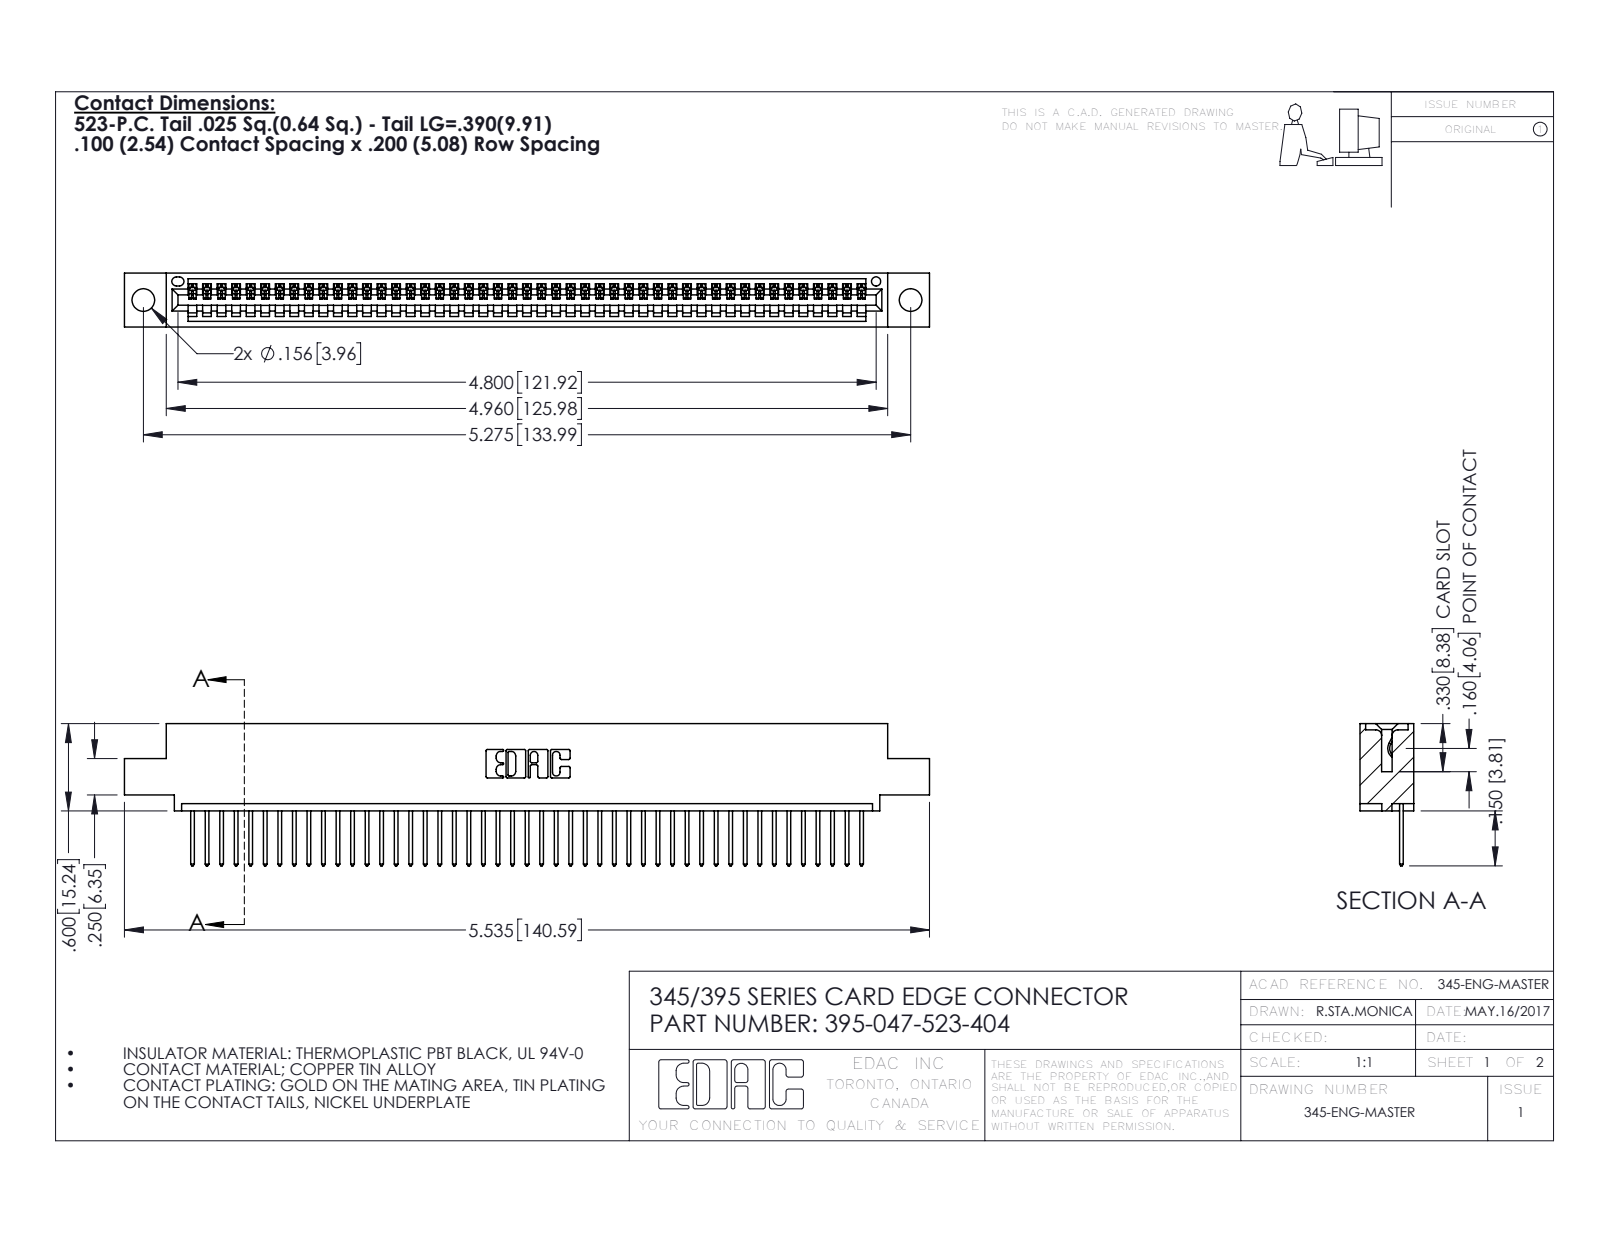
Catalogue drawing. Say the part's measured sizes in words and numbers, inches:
The part is named "345 Part_0.110 Offset - 0.156 Dia-TH; 345-292-001_345-293-123; 395-047-523-404". Its 3-D file was written by "SolidWorks 2016 (CONFIG_CONTROL_DESIGN)". It is 48 solids with 2856 faces: 1964 planar, 892 cylindrical and 0 other. Overall it measures 5.535 by 0.977 by 0.37 inches. Its volume is 0.806 cubic inches and its surface area 27.24 square inches. Round holes: 2 of diameter 0.156, 1 of diameter 0.064. Partial cylindrical surfaces (rounded edges, fillets, slot ends): 94 of radius 0.006, 94 of radius 0.01, 22 of radius 0.01, 6 of radius 0.007, 6 of radius 0.031, 3 of radius 0.026, 2 of radius 0.031, 2 of radius 0.04. The main face-to-face distances are 0.298, 0.072, 0.37, 0.2, 0.098, 0.272, 0.025, 0.225, 0.149, 0.072. The hole center spacings are 0.27, 5.039, 5.275.
